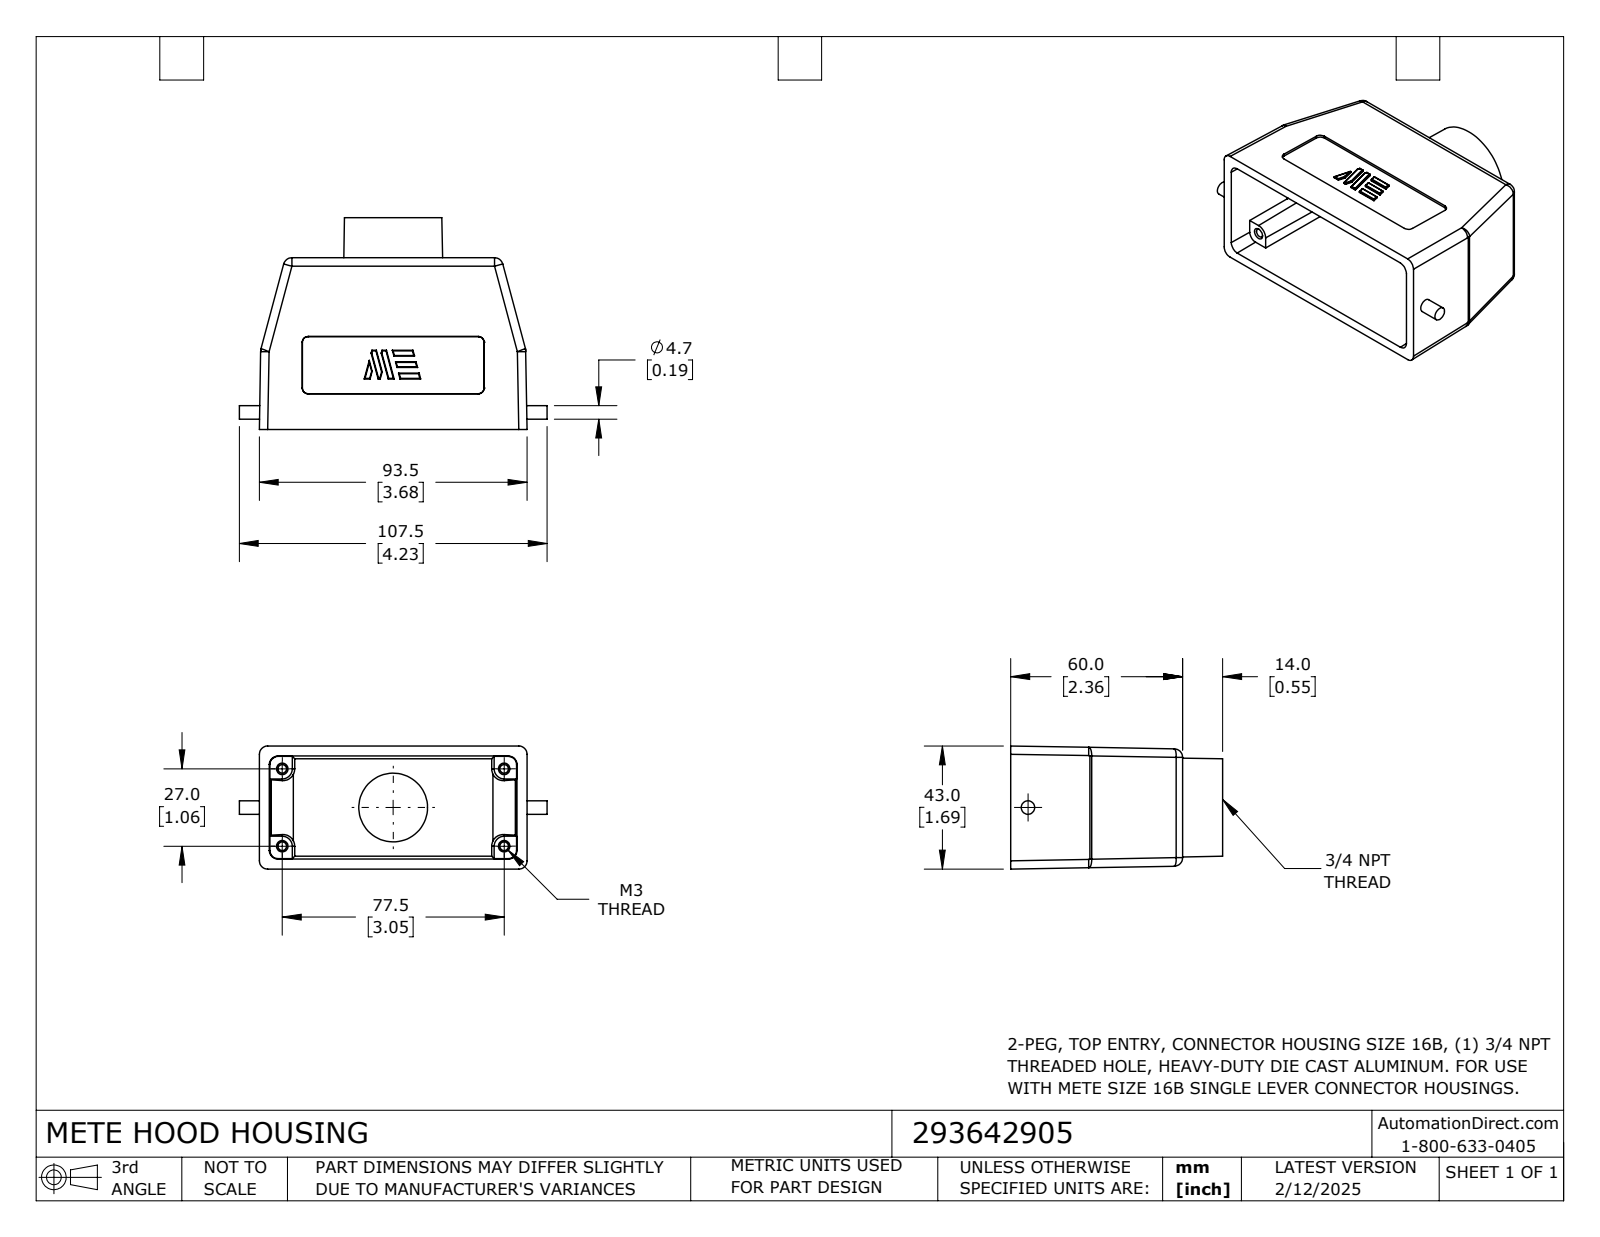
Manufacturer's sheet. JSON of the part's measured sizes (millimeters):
{"part_name": "293642905", "step_written_by": "SolidWorks 2024 (CONFIG_CONTROL_DESIGN)", "units": "millimeters", "bodies": {"solids": 1, "faces": 231, "planar": 111, "cylindrical": 94, "other": 26}, "overall_size": [107.5, 74, 43], "volume_mm3": 67510, "surface_area_mm2": 37860, "round_holes": [[3, 4], [24, 1], [27, 1]], "round_bosses_or_shafts": [[4.7, 1]], "partial_cylinders_radius": [[0.2, 35], [2, 8], [3, 8], [2.9, 6], [2.5, 2]], "face_to_face_distances": [3.5, 2.7, 0.8, 3, 7.8, 11.4, 57, 60, 10.6, 74], "hole_center_spacings": [41, 27, 77.5, 82.1]}
